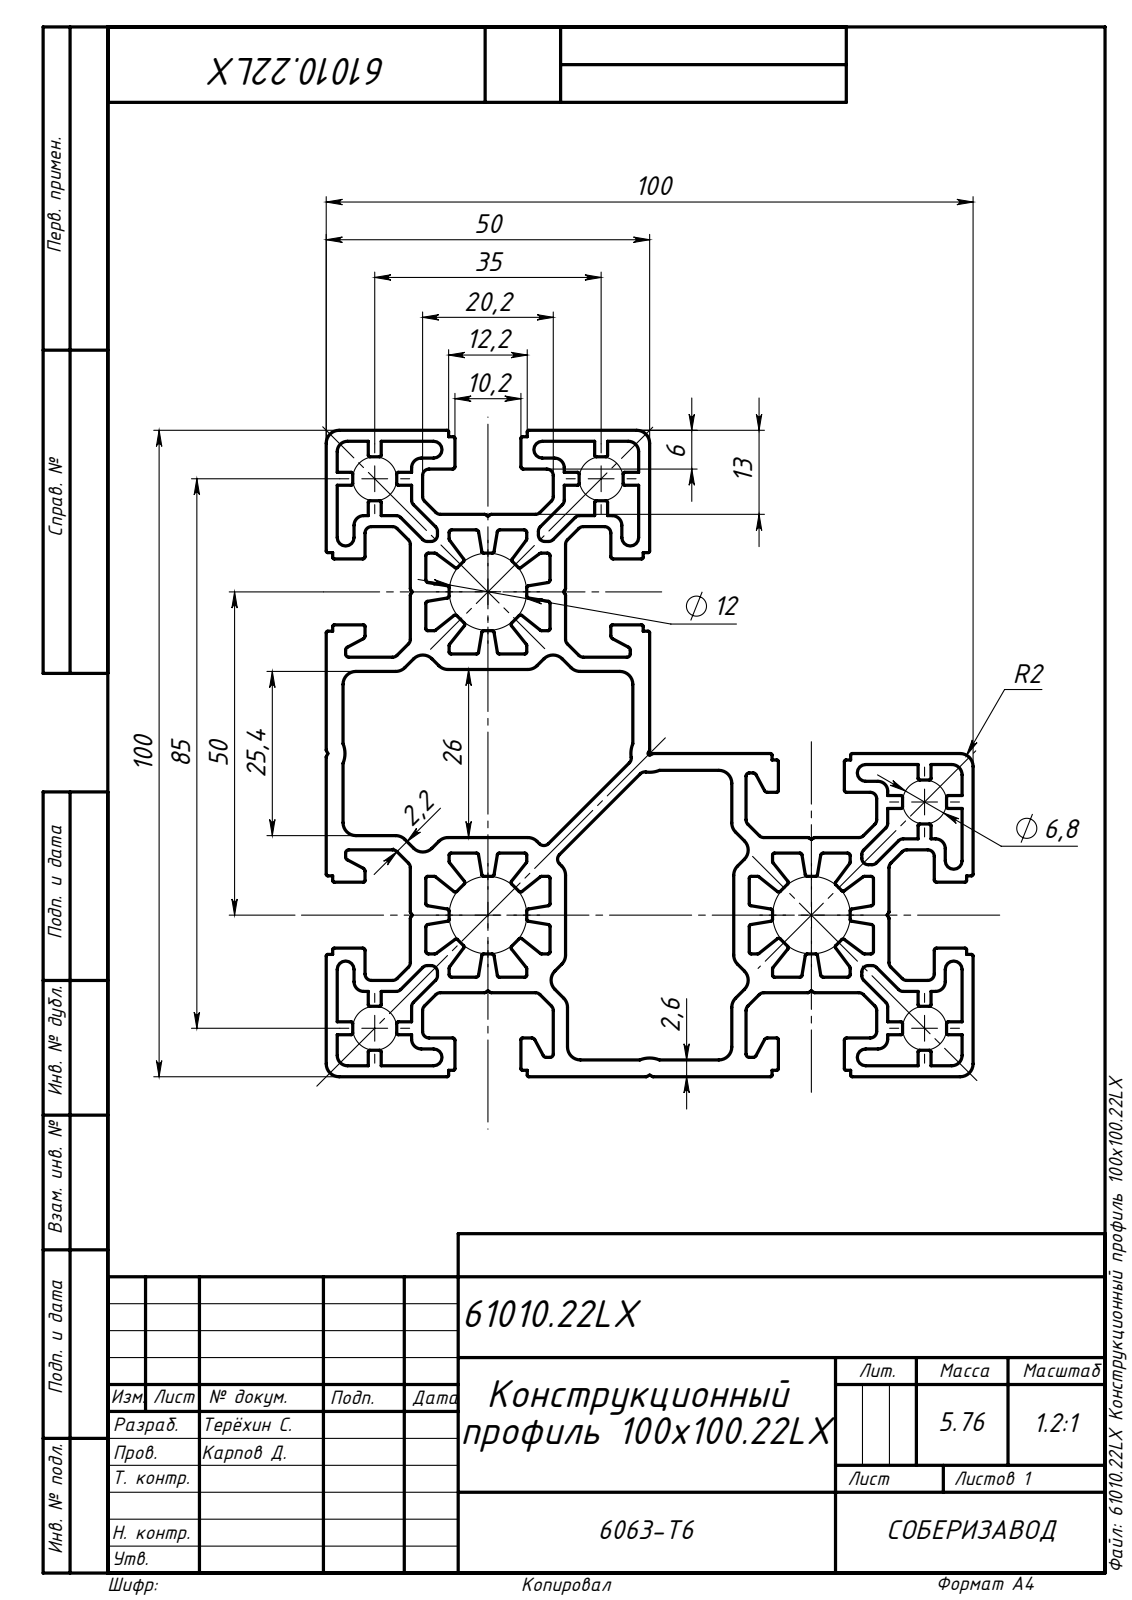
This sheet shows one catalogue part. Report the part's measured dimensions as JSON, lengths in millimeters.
{"step_written_by": "SolidWorks 2020 (AUTOMOTIVE_DESIGN)", "units": "millimeters", "bodies": {"solids": 1, "faces": 854, "planar": 449, "cylindrical": 405, "other": 0}, "overall_size": [1000, 100, 100], "volume_mm3": 2133000, "surface_area_mm2": 1847000, "partial_cylinders_radius": [[0.25, 123], [1, 71], [0.3, 70], [2, 31], [0.4, 30], [0.5, 18], [0.35, 10], [1.3, 10]], "face_to_face_distances": [50, 37, 13, 1.7, 48.3, 35.3, 11.3, 98.3, 32.9, 87]}
